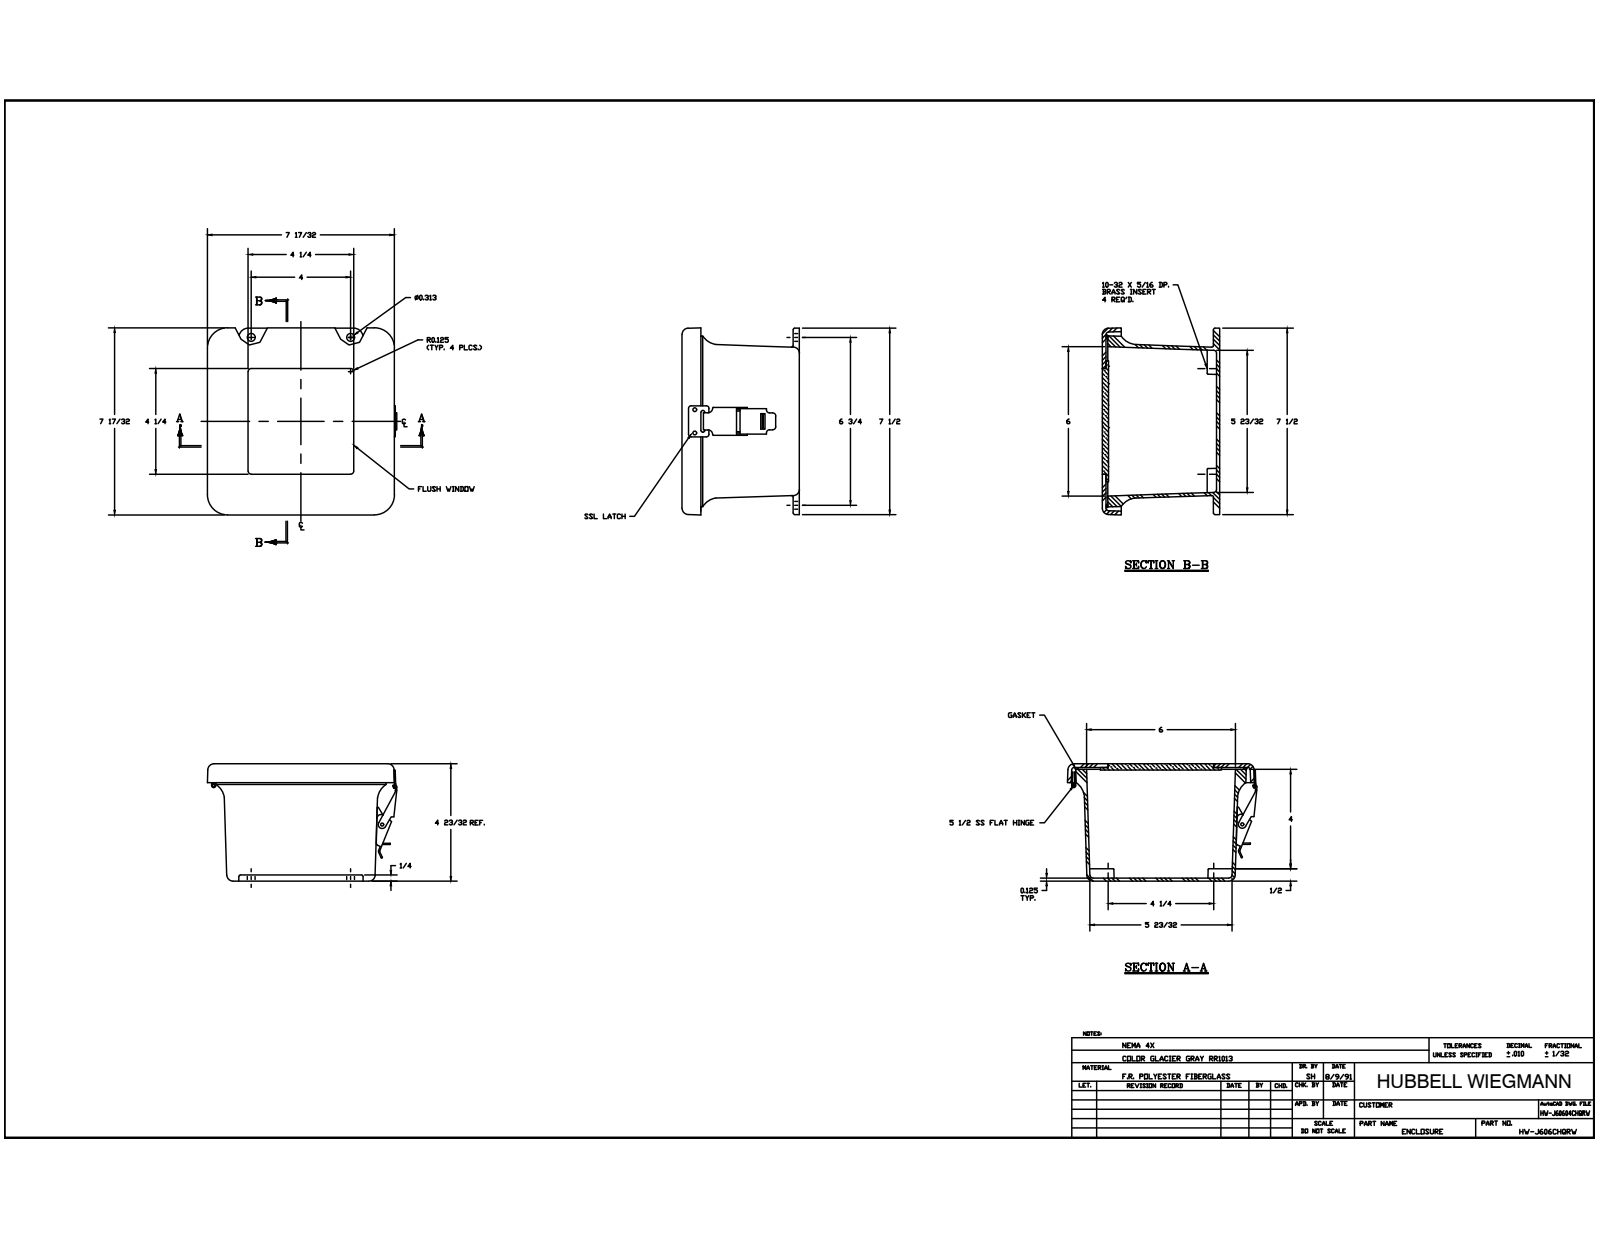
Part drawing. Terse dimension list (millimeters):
name: J606HL_5; RMINS45821P_133; RMINS45821P_134; RMINS45821P_135 (+8 more)
written by: Autodesk Inventor 2014 (AUTOMOTIVE_DESIGN)
unit: mm
bodies: 26 solids, 658 faces (264 planar, 270 cylindrical, 124 other)
size: 193.41 × 191.13 × 122.52
volume: 664 379 mm³; area: 345 468 mm²
holes: 11× ⌀3.56, 5× ⌀3.33, 5× ⌀3.86, 4× ⌀2.64, 4× ⌀3.96, 4× ⌀5.54, 2× ⌀3.3, 2× ⌀3.43, 1× ⌀2.16, 1× ⌀9.52
bosses: 9× ⌀3.17, 5× ⌀6.35, 4× ⌀6.86, 1× ⌀7.62, 1× ⌀4.31, 1× ⌀3.94, 1× ⌀3.05
rounds: 20× R0.79, 16× R3.17, 16× R6.35, 12× R0.38, 8× R1.14, 6× R0.76, 5× R0.57, 5× R5.08
face distances: 3.74, 118.78, 122.52, 6.35, 116.17, 3.17, 115.61, 119.35, 113, 2.61
hole spacings: 134.82, 23.81, 34.8, 63.5, 107.94, 157.16, 187.45, 19.05
